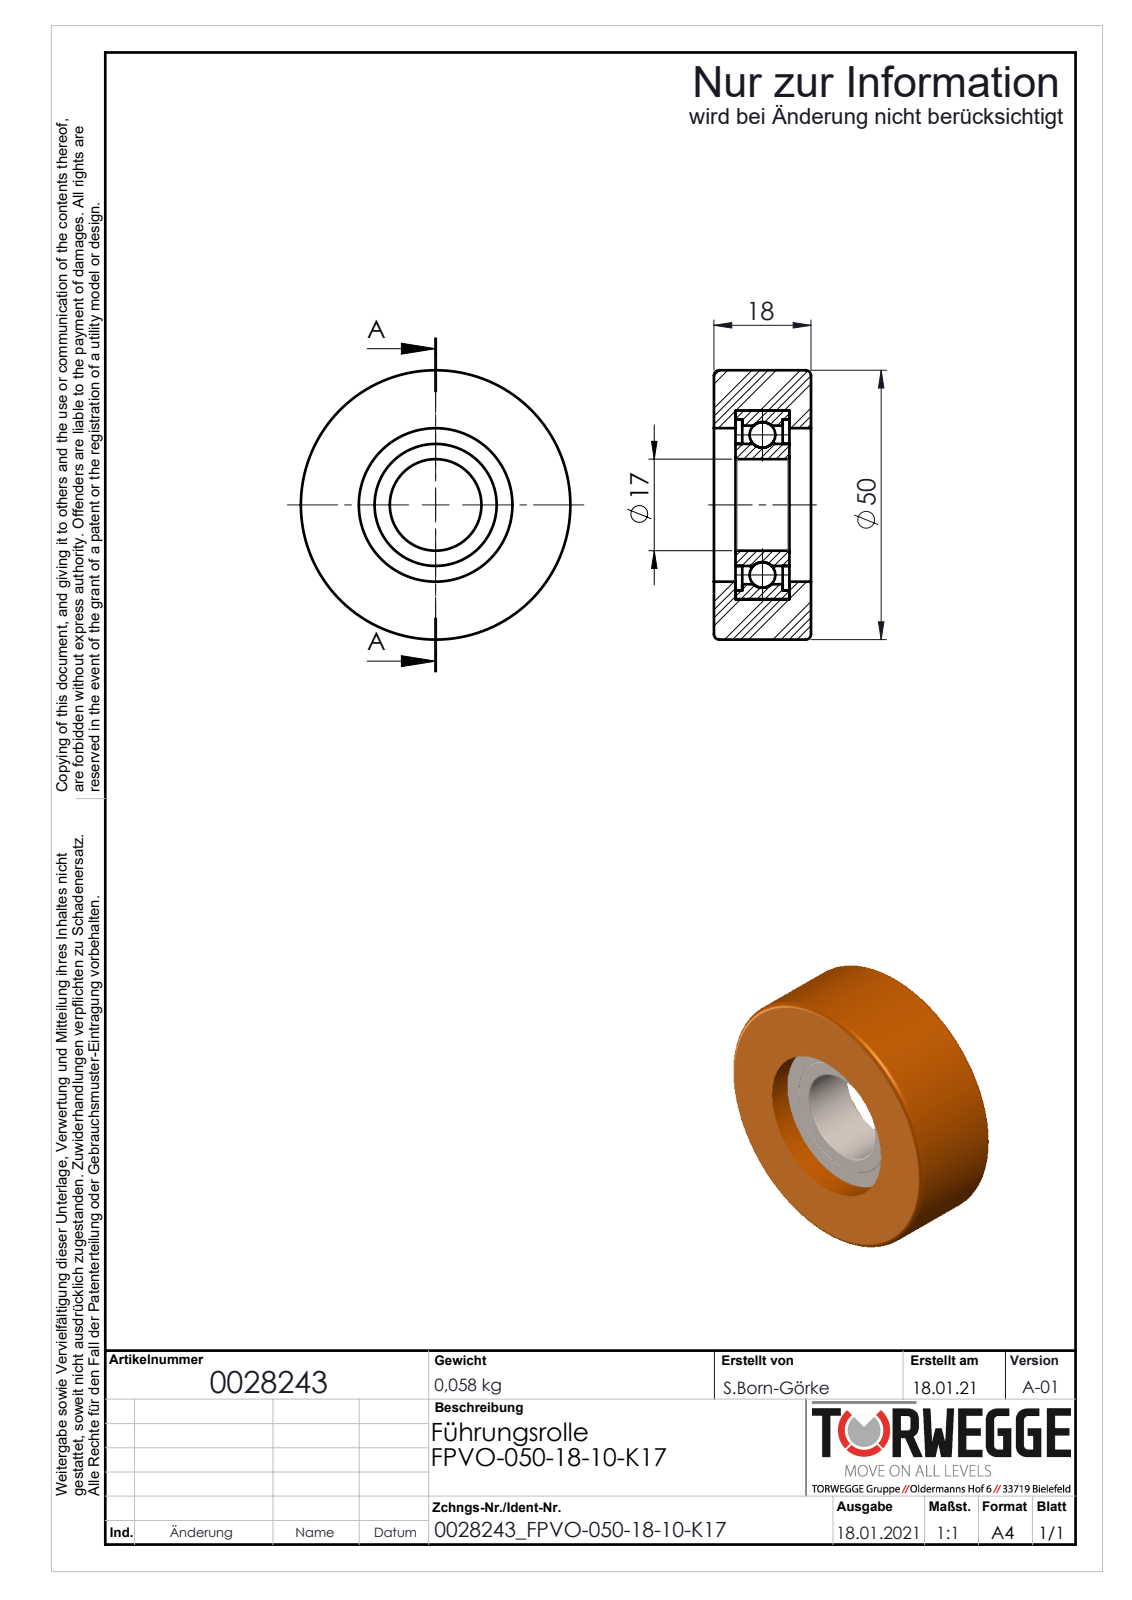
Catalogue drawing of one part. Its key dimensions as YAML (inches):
part_name: "0028243"
step_written_by: "SolidWorks 2018 (AUTOMOTIVE_DESIGN)"
units: inches
bodies: {solids: 15, faces: 88, planar: 14, cylindrical: 32, other: 42}
overall_size: [1.969, 1.969, 0.709]
volume: 1.594
surface_area: 22.79
round_holes:
  - {diameter: 0.669, count: 1}
  - {diameter: 0.892, count: 1}
  - {diameter: 1.122, count: 1}
  - {diameter: 1.159, count: 1}
  - {diameter: 1.248, count: 1}
  - {diameter: 1.378, count: 1}
round_bosses_or_shafts:
  - {diameter: 1.969, count: 1}
face_to_face_distances: [0.157, 0.551, 0.709, 0.394, 0.207, 0.502, 0.049, 0.344, 0.295]
